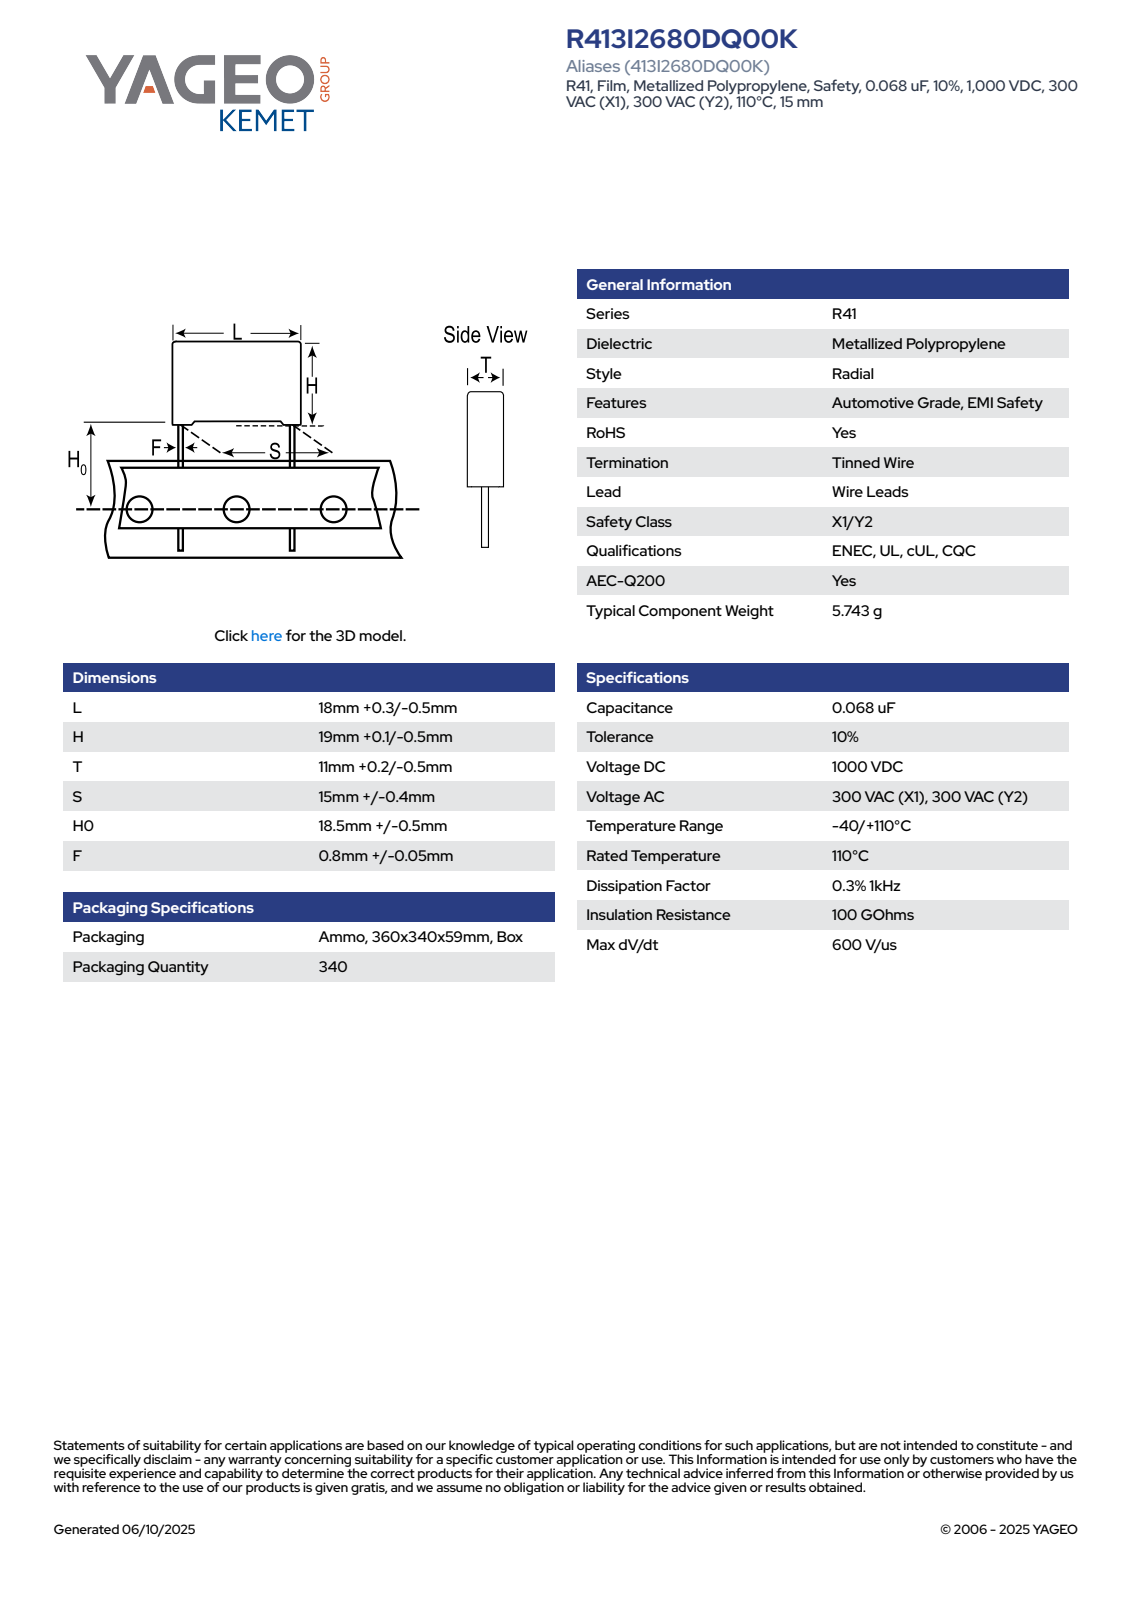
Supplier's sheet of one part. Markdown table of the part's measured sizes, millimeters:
| quantity | value |
| --- | --- |
| part name | CFR_RB2_18X19X11_L18.3H19.1T11.2S15H019F0.85 |
| STEP written by | SolidWorks 2020 (AUTOMOTIVE_DESIGN) |
| units | millimeters |
| bodies | 4 solids, 85 faces (77 planar, 8 cylindrical, 0 other) |
| overall size | 38.1 × 18.3 × 11.21 |
| volume | 3 797 mm³ |
| surface area | 1 666 mm² |
| round bosses / shafts (diameter × count) | 0.85 × 2 |
| partial cylindrical surfaces (radius × count) | 0.5 × 4 |
| main face-to-face distances | 11.2, 18.3, 18.35, 0.61, 0.75, 19.1, 17.69, 0.66, 18.44, 10.59 |
